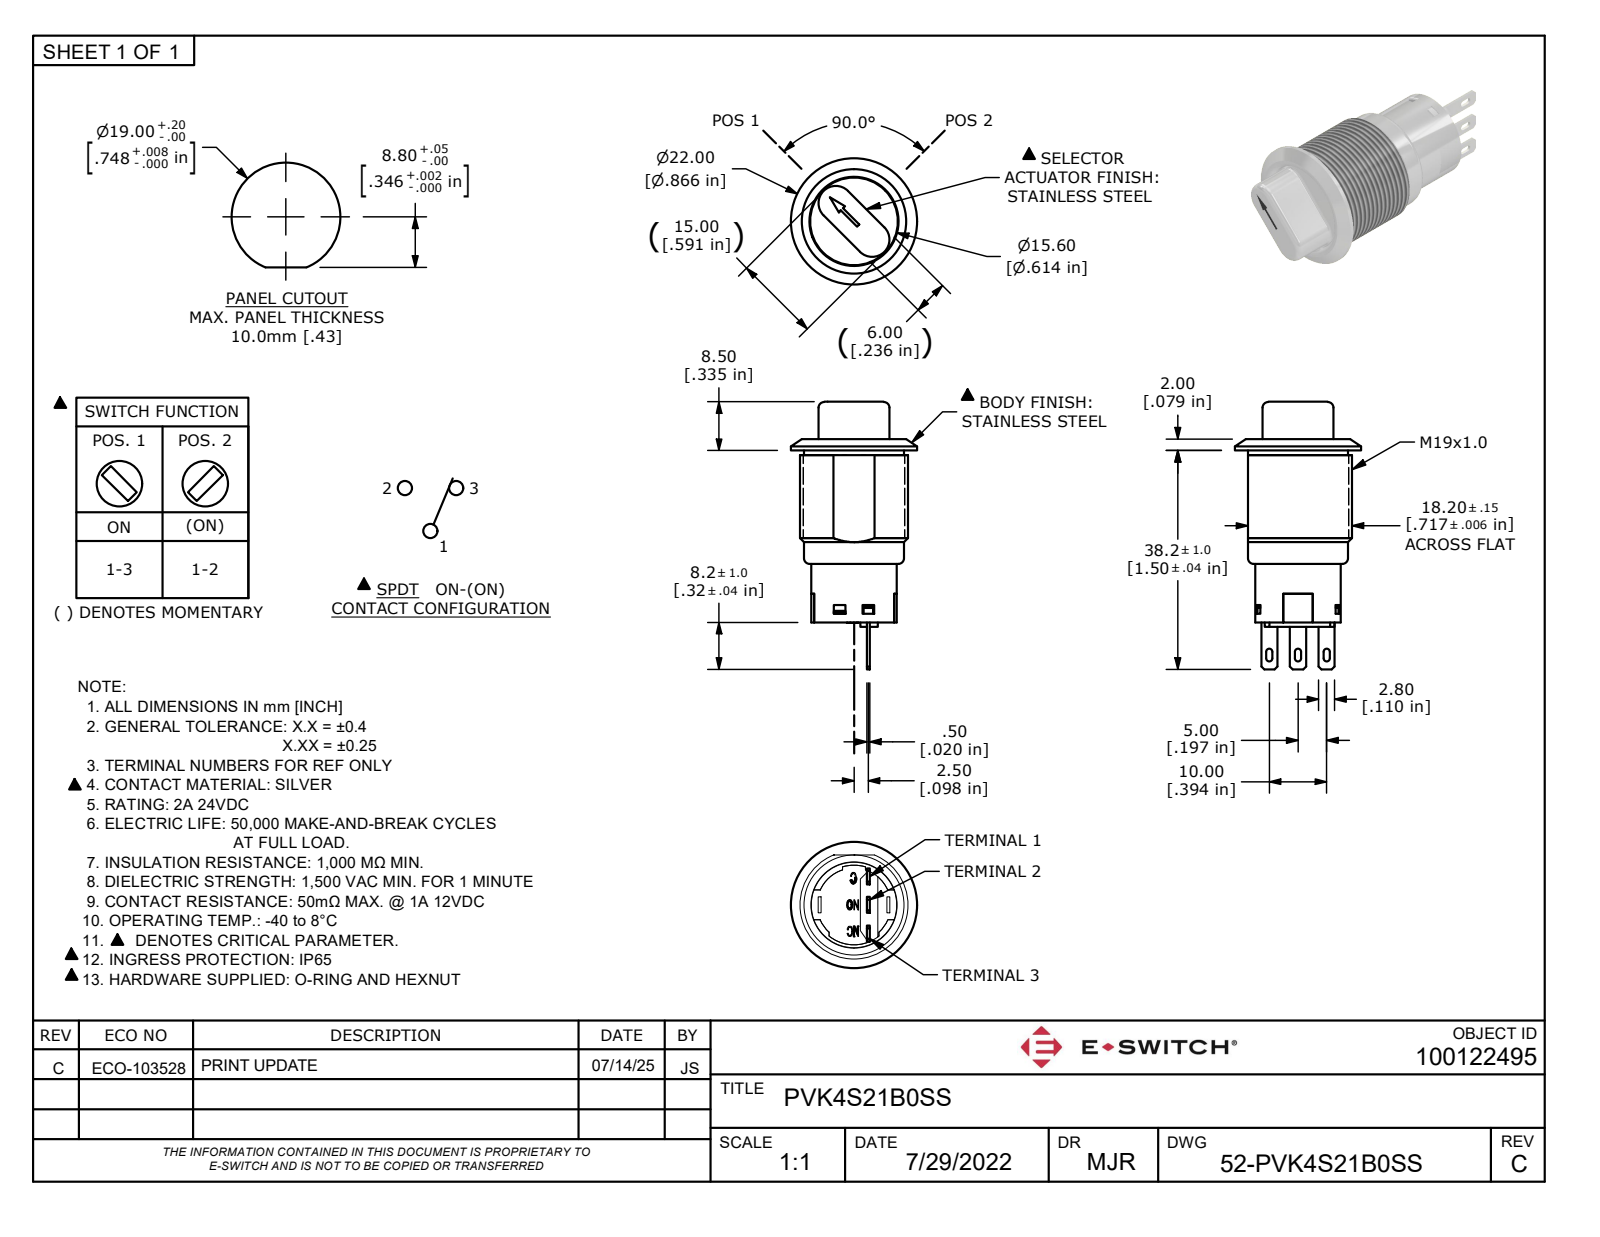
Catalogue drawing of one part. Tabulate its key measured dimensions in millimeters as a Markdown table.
| quantity | value |
| --- | --- |
| part name | PVK4S21x0SS |
| STEP written by | Autodesk Inventor 2020 (AUTOMOTIVE_DESIGN) |
| units | millimeters |
| bodies | 2 solids, 217 faces (137 planar, 35 cylindrical, 45 other) |
| overall size | 46.7 × 22 × 22 |
| volume | 10 045 mm³ |
| surface area | 3 763 mm² |
| round holes (diameter × count) | 15 × 1, 17.5 × 1, 22 × 1 |
| round bosses / shafts (diameter × count) | 18.9 × 1, 15.6 × 1, 15.3 × 1, 14.9 × 1, 14.5 × 1 |
| partial cylindrical surfaces (radius × count) | 0.55 × 6, 0.5 × 2, 1 × 2, 3 × 2, 6.45 × 1, 6.95 × 1 |
| main face-to-face distances | 0.4, 15.7, 15.3, 30.4, 14.7, 30.8, 16.1, 0.5, 6, 1.5 |
